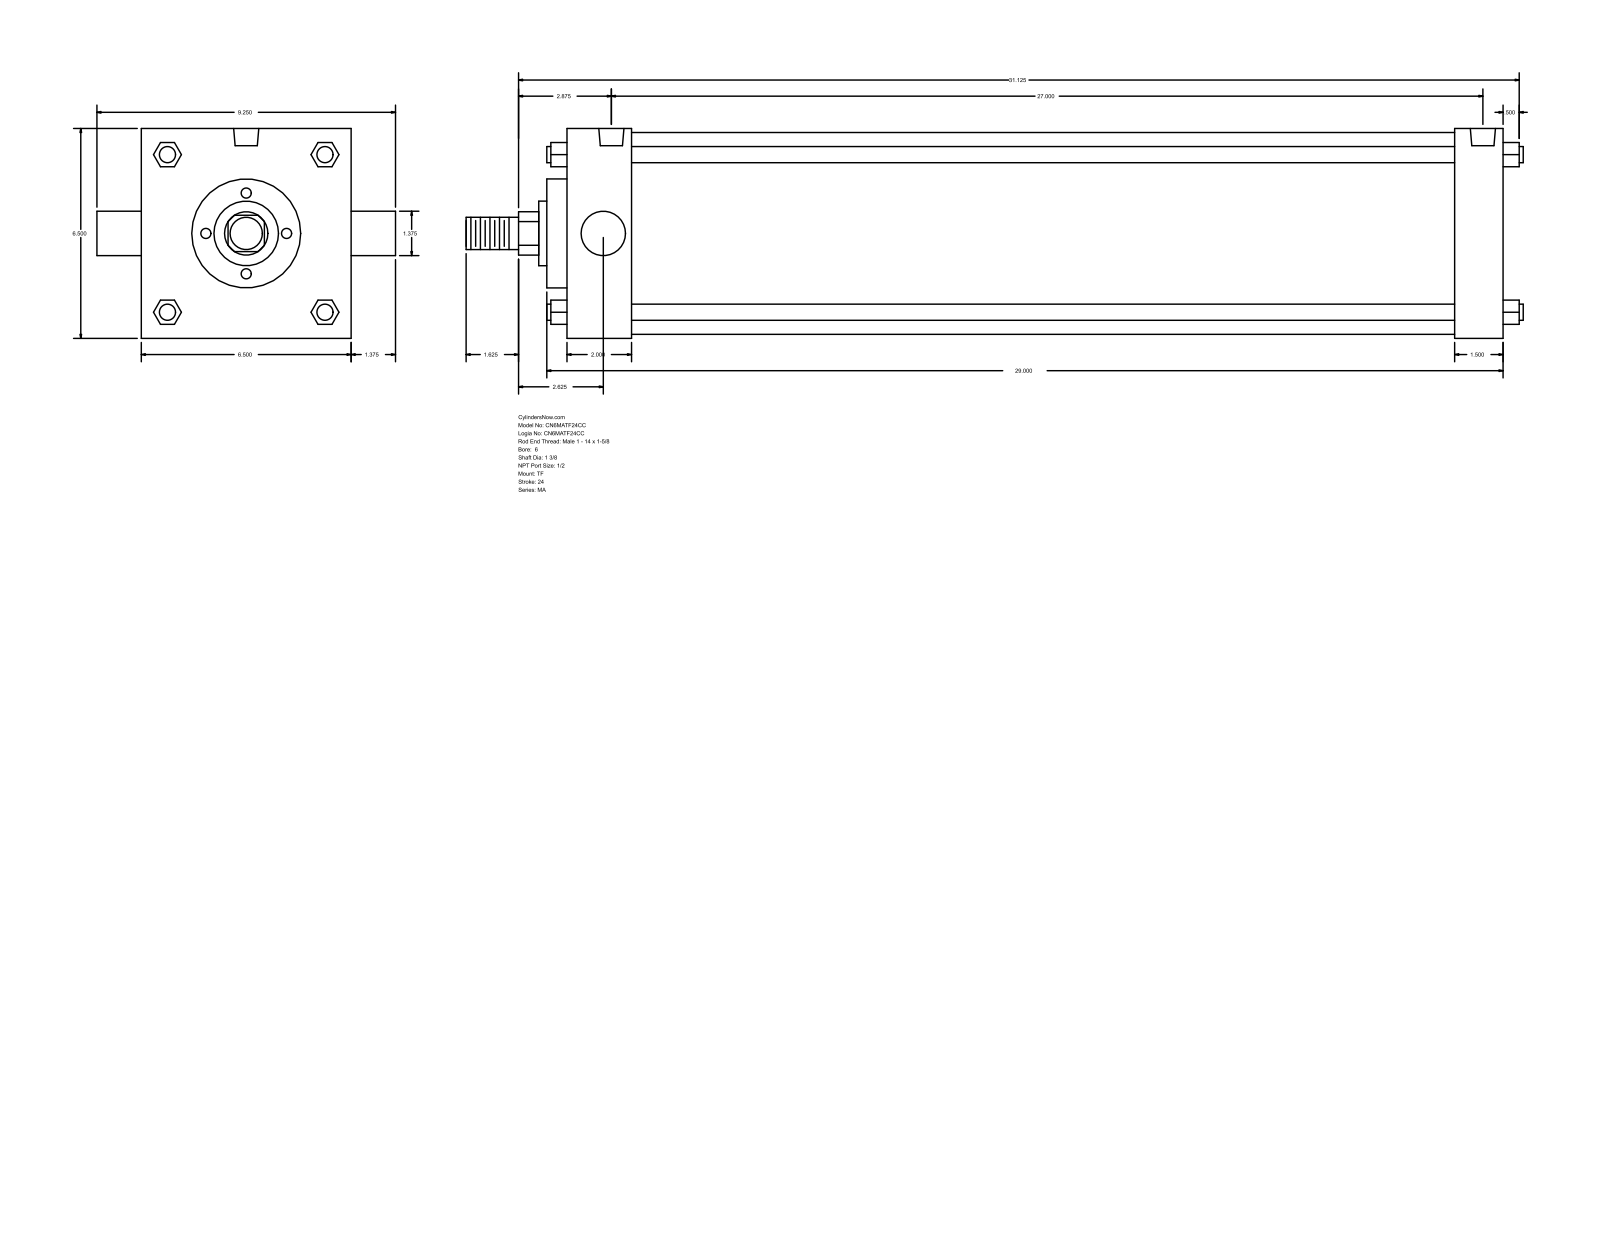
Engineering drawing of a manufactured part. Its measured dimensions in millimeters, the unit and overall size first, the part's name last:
Units: millimetres
Overall size (bounding box): 831.85 × 234.95 × 165.1
Round holes (diameter × count): ⌀17.46 ×3, ⌀19.77 ×2
Round bosses / shafts (diameter × count): ⌀12.7 ×4, ⌀34.92 ×2, ⌀158.75 ×1, ⌀85.72 ×1, ⌀50.8 ×1, ⌀25.4 ×1
Partial cylindrical surfaces — rounded edges, fillets, slot ends (radius × count): R17.06 ×1
Main face-to-face distances: 165.1, 739.78, 50.8, 688.98, 701.67, 650.87, 38.11, 66.67, 15.87, 717.54
Hole centre spacings: 3.18, 685.8, 688.98
Bodies: 0 solids, 122 faces (93 planar, 29 cylindrical, 0 other)
Part name (STEP PRODUCT): MA_TF__0600_1.375
STEP written by: GSSL Pune (CONFIG_CONTROL_DESIGN)
